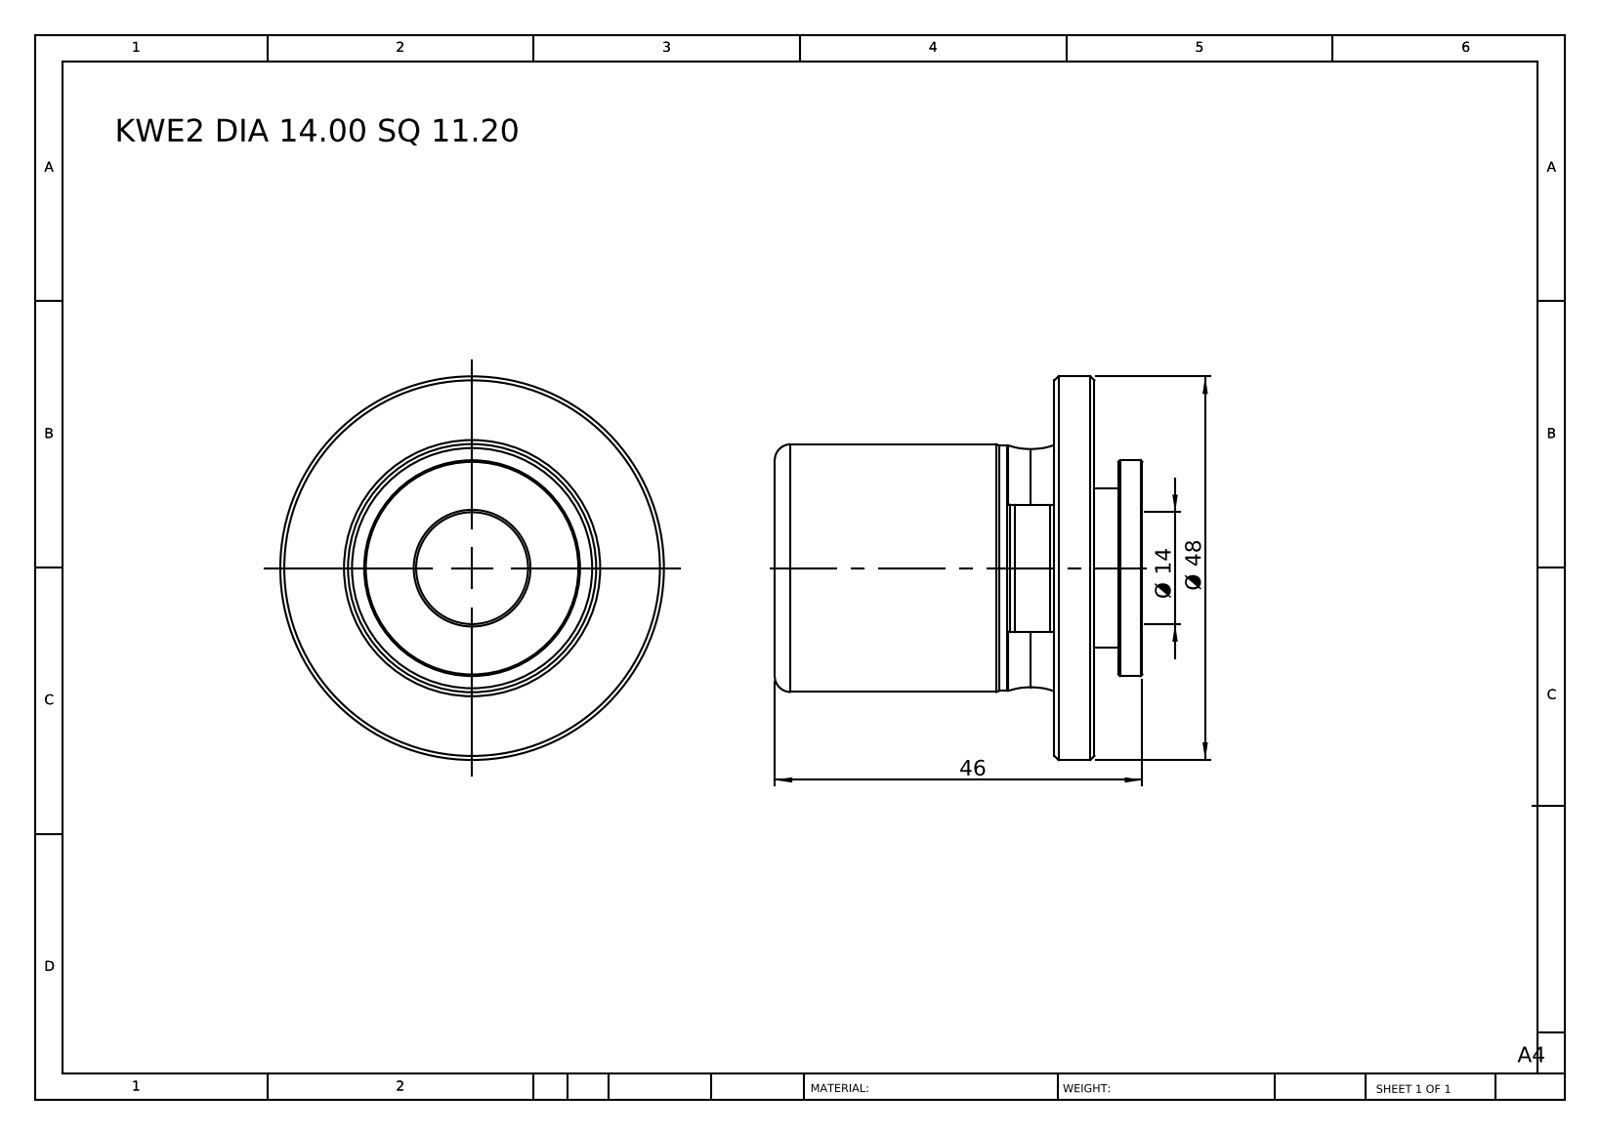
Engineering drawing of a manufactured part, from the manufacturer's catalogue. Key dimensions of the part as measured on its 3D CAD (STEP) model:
Part name (STEP PRODUCT): KWE2 DIA 14.00 SQ 11.20
STEP written by: SolidWorks 2014 (CONFIG_CONTROL_DESIGN)
Units: millimetres
Bodies: 1 solid, 61 faces (13 planar, 18 cylindrical, 30 other)
Overall size (bounding box): 48 × 48 × 46
Volume: 34 276 mm³ · Surface area: 9 975 mm²
Round holes (diameter × count): ⌀14 ×1
Round bosses / shafts (diameter × count): ⌀48 ×1, ⌀31 ×1, ⌀30.7 ×1, ⌀27 ×1, ⌀20 ×1
Partial cylindrical surfaces — rounded edges, fillets, slot ends (radius × count): R15.53 ×1, R19.9 ×1
Main face-to-face distances: 5, 35, 40, 3, 46, 11, 6, 43, 8, 18
